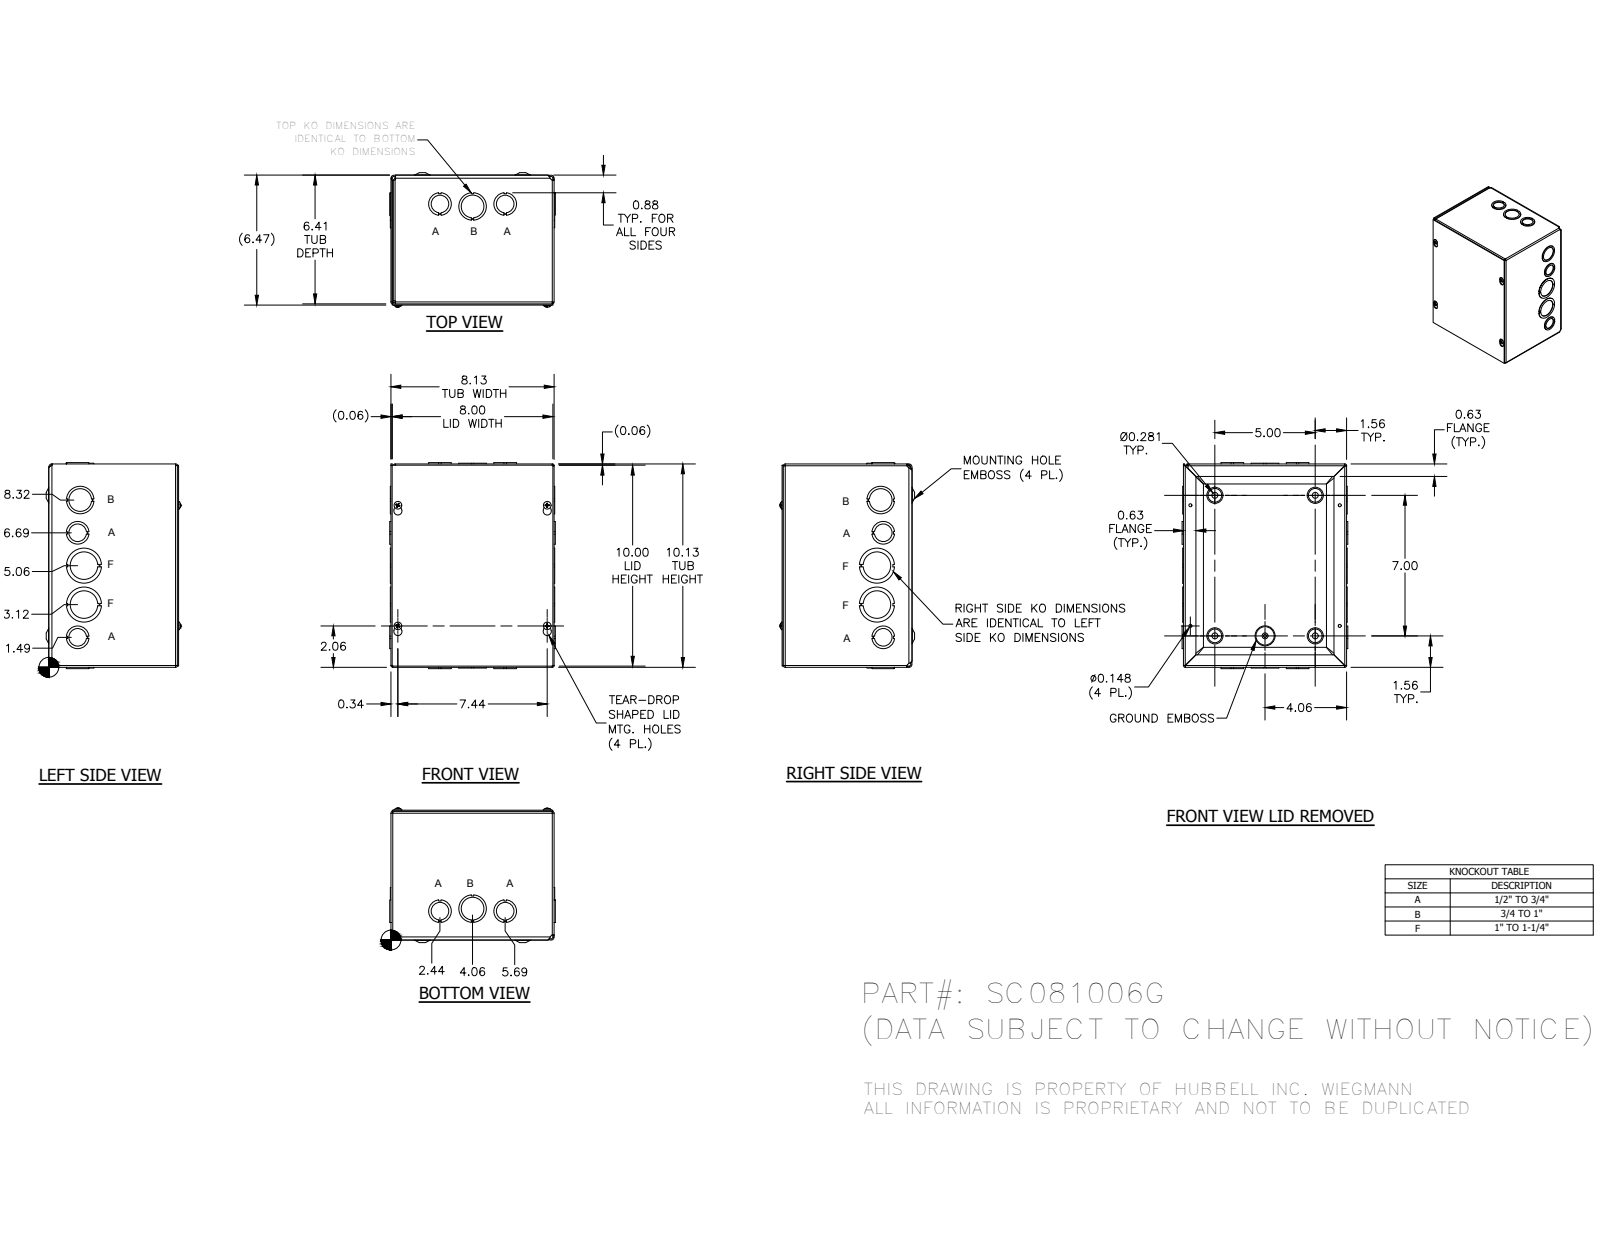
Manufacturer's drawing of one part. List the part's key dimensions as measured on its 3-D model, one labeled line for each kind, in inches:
Part name (STEP PRODUCT): SC0810GBKP; SC081006GWRA; SC0810GLID; 34056 (+1 more)
STEP written by: Autodesk Inventor 2014 (AUTOMOTIVE_DESIGN)
Units: inches
Bodies: 22 solids, 806 faces (486 planar, 169 cylindrical, 151 other)
Overall size (bounding box): 10.249 × 8.249 × 6.693
Round holes (diameter × count): ⌀1.125 ×6, ⌀0.148 ×4, ⌀0.3 ×4, ⌀0.875 ×4, ⌀1.375 ×4, ⌀1.75 ×2, ⌀0.165 ×1
Round bosses / shafts (diameter × count): ⌀0.384 ×4, ⌀0.164 ×4, ⌀0.228 ×1
Partial cylindrical surfaces — rounded edges, fillets, slot ends (radius × count): R0.031 ×8, R0.093 ×8, R0.055 ×4, R0.062 ×4, R0.094 ×4, R0.11 ×4, R0.117 ×4, R0.124 ×4
Main face-to-face distances: 0.062, 0.062, 6.343, 6.405, 0.063, 6.406, 6.468, 8.125, 8.063, 8.063
Hole centre spacings: 6.613, 8.996, 1.317, 1.317, 1.659, 2.5, 3.584, 5
